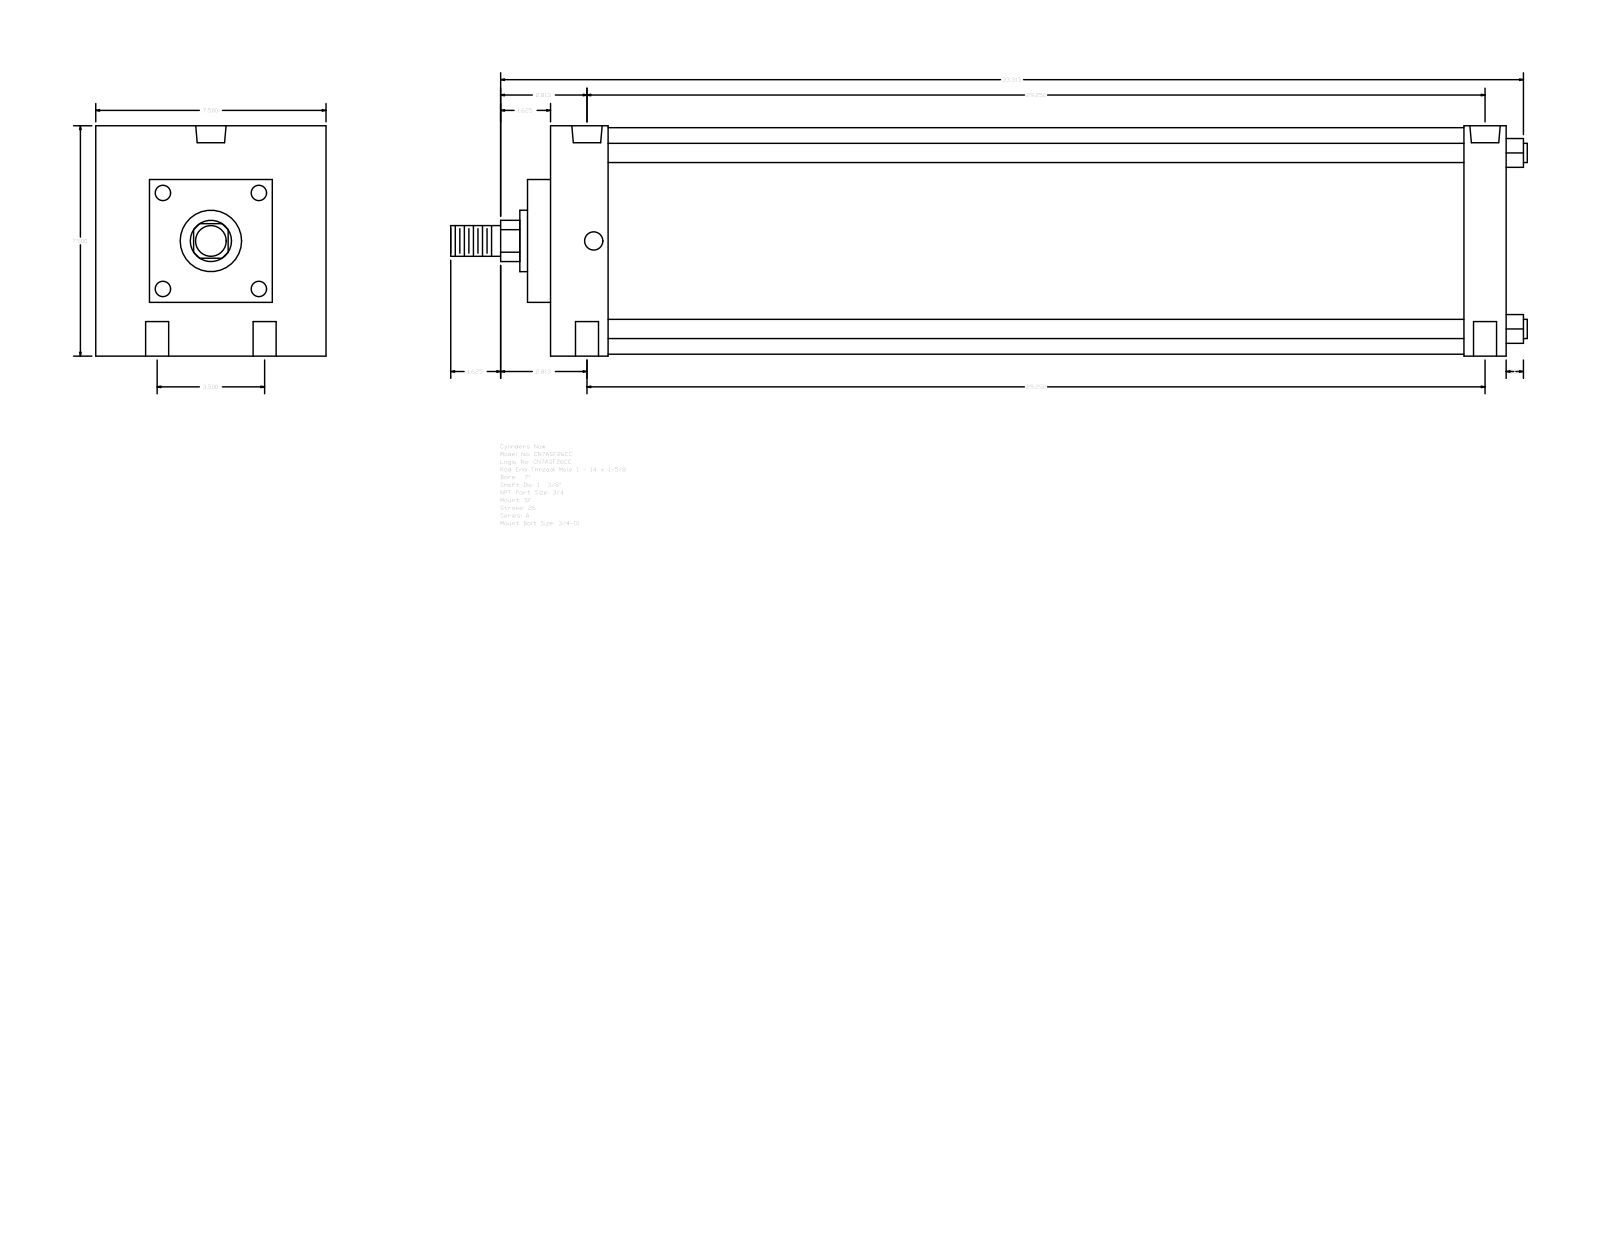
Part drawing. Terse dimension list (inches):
name: A_SF__0700_1.375
written by: GSSL Pune (CONFIG_CONTROL_DESIGN)
unit: in
bodies: 0 solids, 93 faces (67 planar, 26 cylindrical, 0 other)
size: 35.063 × 7.5 × 7.5
holes: 4× ⌀0.75, 2× ⌀0.594, 2× ⌀0.989
bosses: 4× ⌀0.625, 1× ⌀7.375, 1× ⌀2, 1× ⌀1.375, 1× ⌀1
rounds: 1× R0.672
face distances: 7.5, 31.125, 0.75, 31.875, 2.625, 30.5, 1.875, 29.75, 27.875, 29.25
hole spacings: 1.75, 29.302, 29.25, 3.5, 29.459, 28.812
